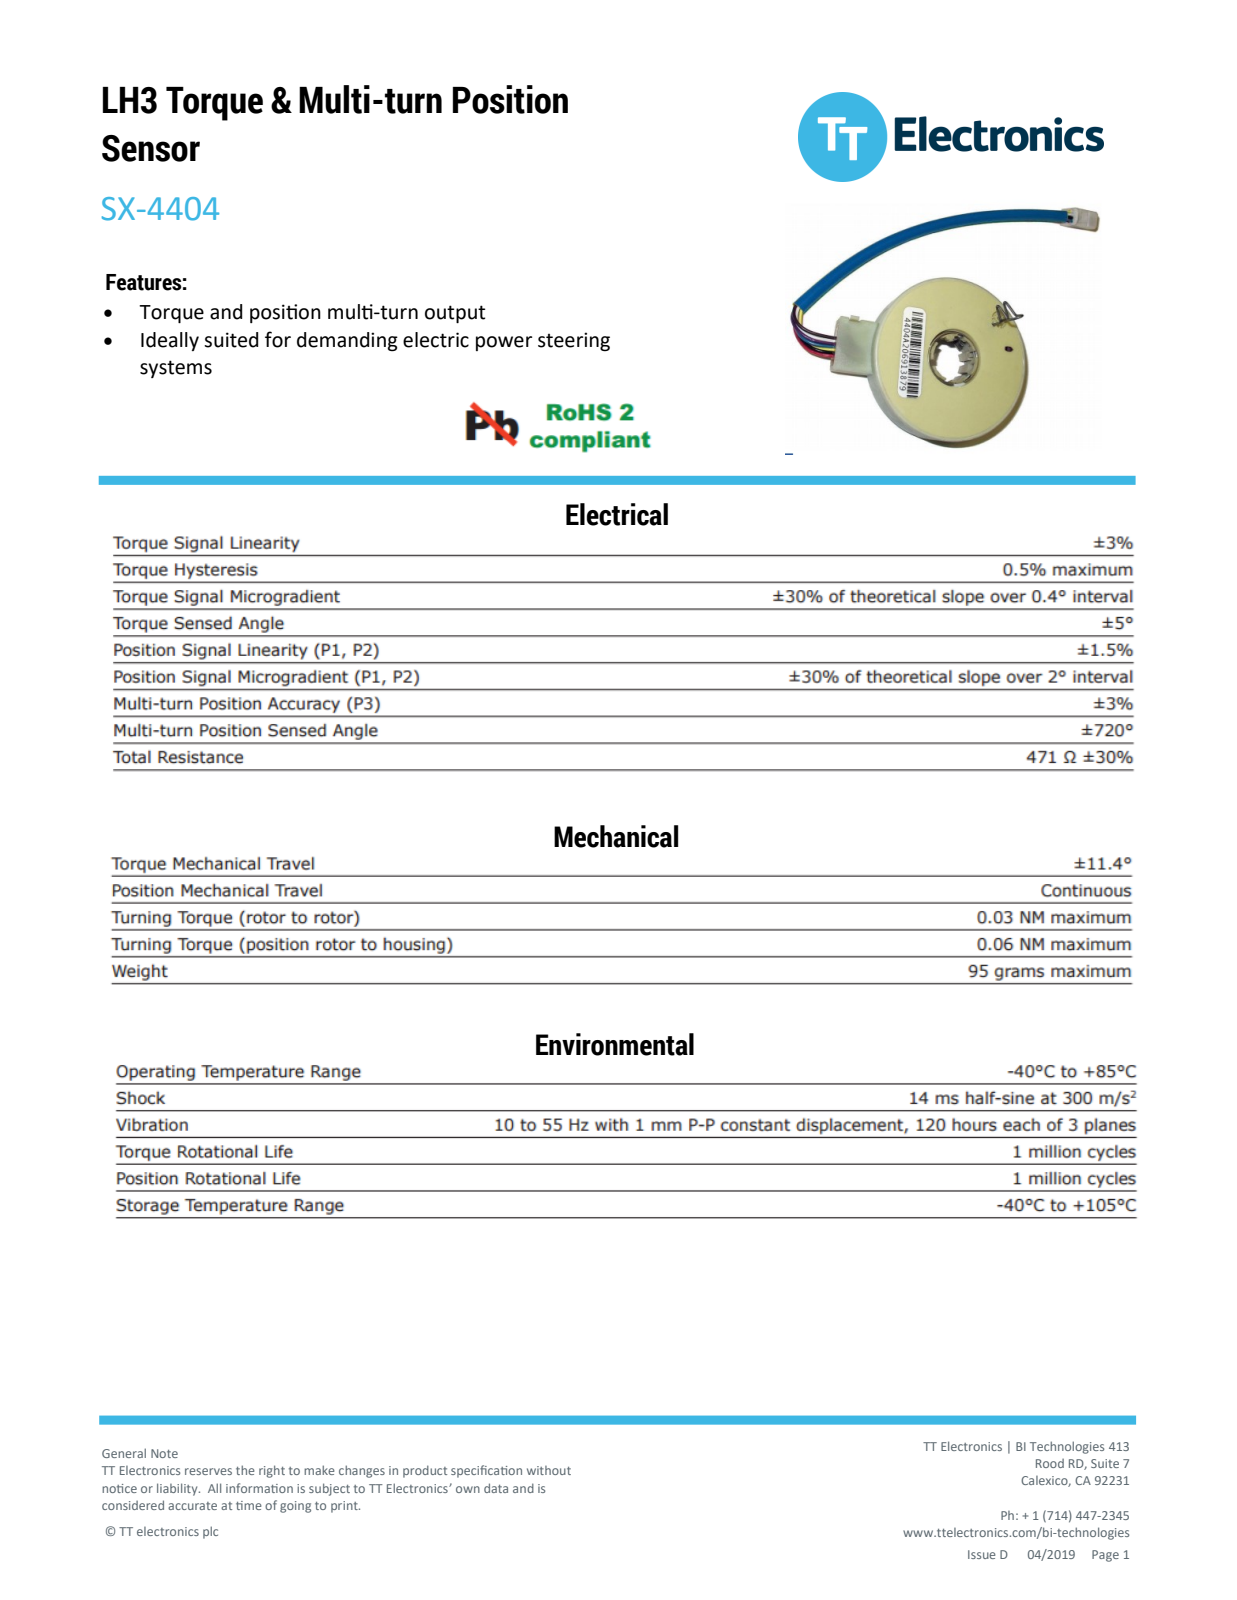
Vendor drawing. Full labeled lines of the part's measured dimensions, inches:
Part name (STEP PRODUCT): SX-4404A_SW0001
STEP written by: CREO PARAMETRIC BY PTC INC, 2016390 (CONFIG_CONTROL_DESIGN)
Units: inches
Bodies: 3 solids, 1941 faces (983 planar, 642 cylindrical, 316 other)
Overall size (bounding box): 13.21 × 3.2 × 1.728
Volume: 5.826 in³ · Surface area: 47.75 in²
Round holes (diameter × count): ⌀0.032 ×8, ⌀0.042 ×7, ⌀0.039 ×5, ⌀0.985 ×1, ⌀1.046 ×1, ⌀1.126 ×1, ⌀1.146 ×1, ⌀1.2 ×1, ⌀1.255 ×1
Round bosses / shafts (diameter × count): ⌀0.062 ×21, ⌀0.025 ×14, ⌀0.047 ×6, ⌀3.2 ×1, ⌀1.345 ×1, ⌀1.234 ×1, ⌀0.26 ×1, ⌀0.046 ×1
Partial cylindrical surfaces — rounded edges, fillets, slot ends (radius × count): R0.007 ×72, R0.012 ×72, R0.005 ×44, R0.01 ×30, R0.02 ×21, R0.016 ×19, R0.006 ×18, R0.028 ×18
Main face-to-face distances: 0.719, 0.065, 0.108, 0.784, 0.012, 0.043, 0.521, 0.724, 0.531, 0.077
Hole centre spacings: 0.087, 0.115, 0.146, 0.118, 0.173, 0.21, 0.23, 0.093
